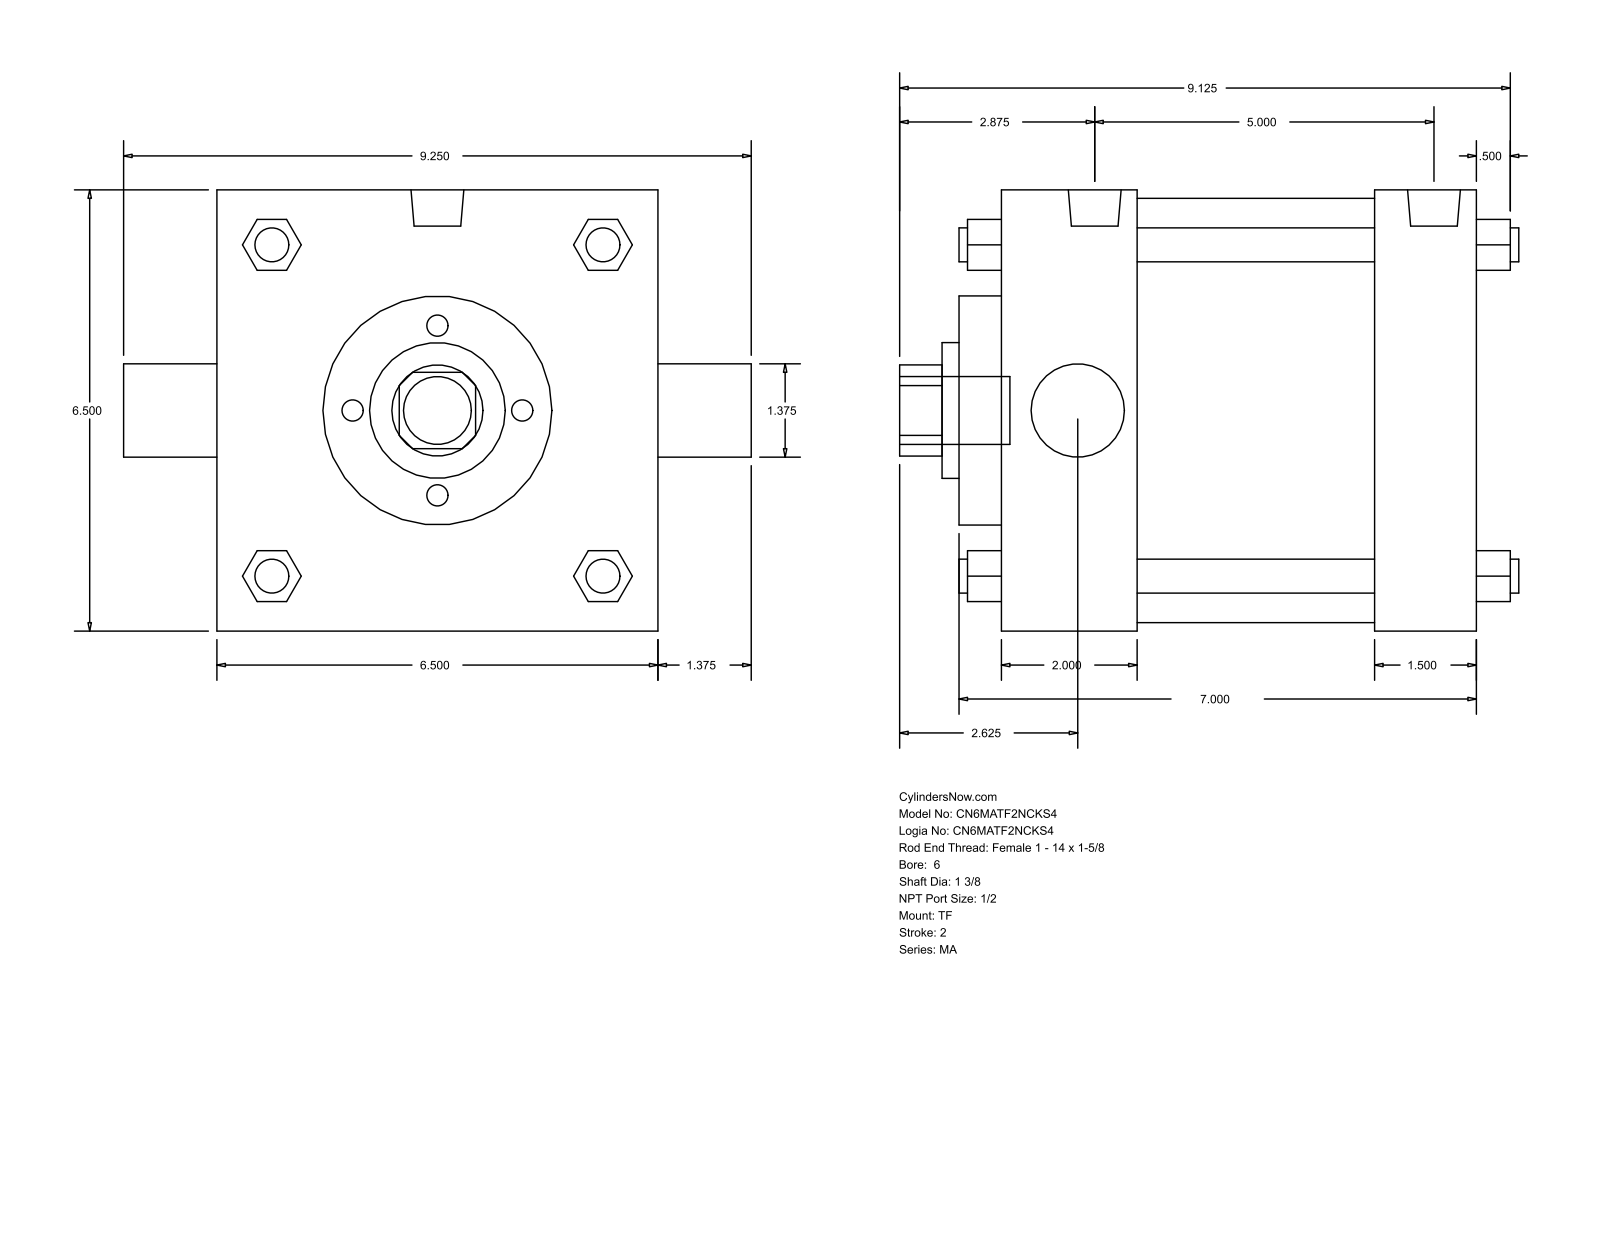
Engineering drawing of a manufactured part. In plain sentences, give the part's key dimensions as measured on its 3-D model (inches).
The part is named "MA_TF__0600_1.375". Its 3-D file was written by "GSSL Pune (CONFIG_CONTROL_DESIGN)". It is 0 solids with 122 faces: 93 planar, 29 cylindrical and 0 other. Overall it measures 9.25 by 9.125 by 6.5 inches. Round holes: 2 of diameter 1.375, 1 of diameter 2, 1 of diameter 3.375, 1 of diameter 6.25. Round bosses or shafts: 4 of diameter 0.5, 3 of diameter 0.687, 2 of diameter 0.778, 1 of diameter 1. Partial cylindrical surfaces (rounded edges, fillets, slot ends): 1 of radius 0.672. The main face-to-face distances are 6.5, 7.125, 1.5, 2, 5.125, 5.625, 3.625, 0.625, 2.625, 6.25.
